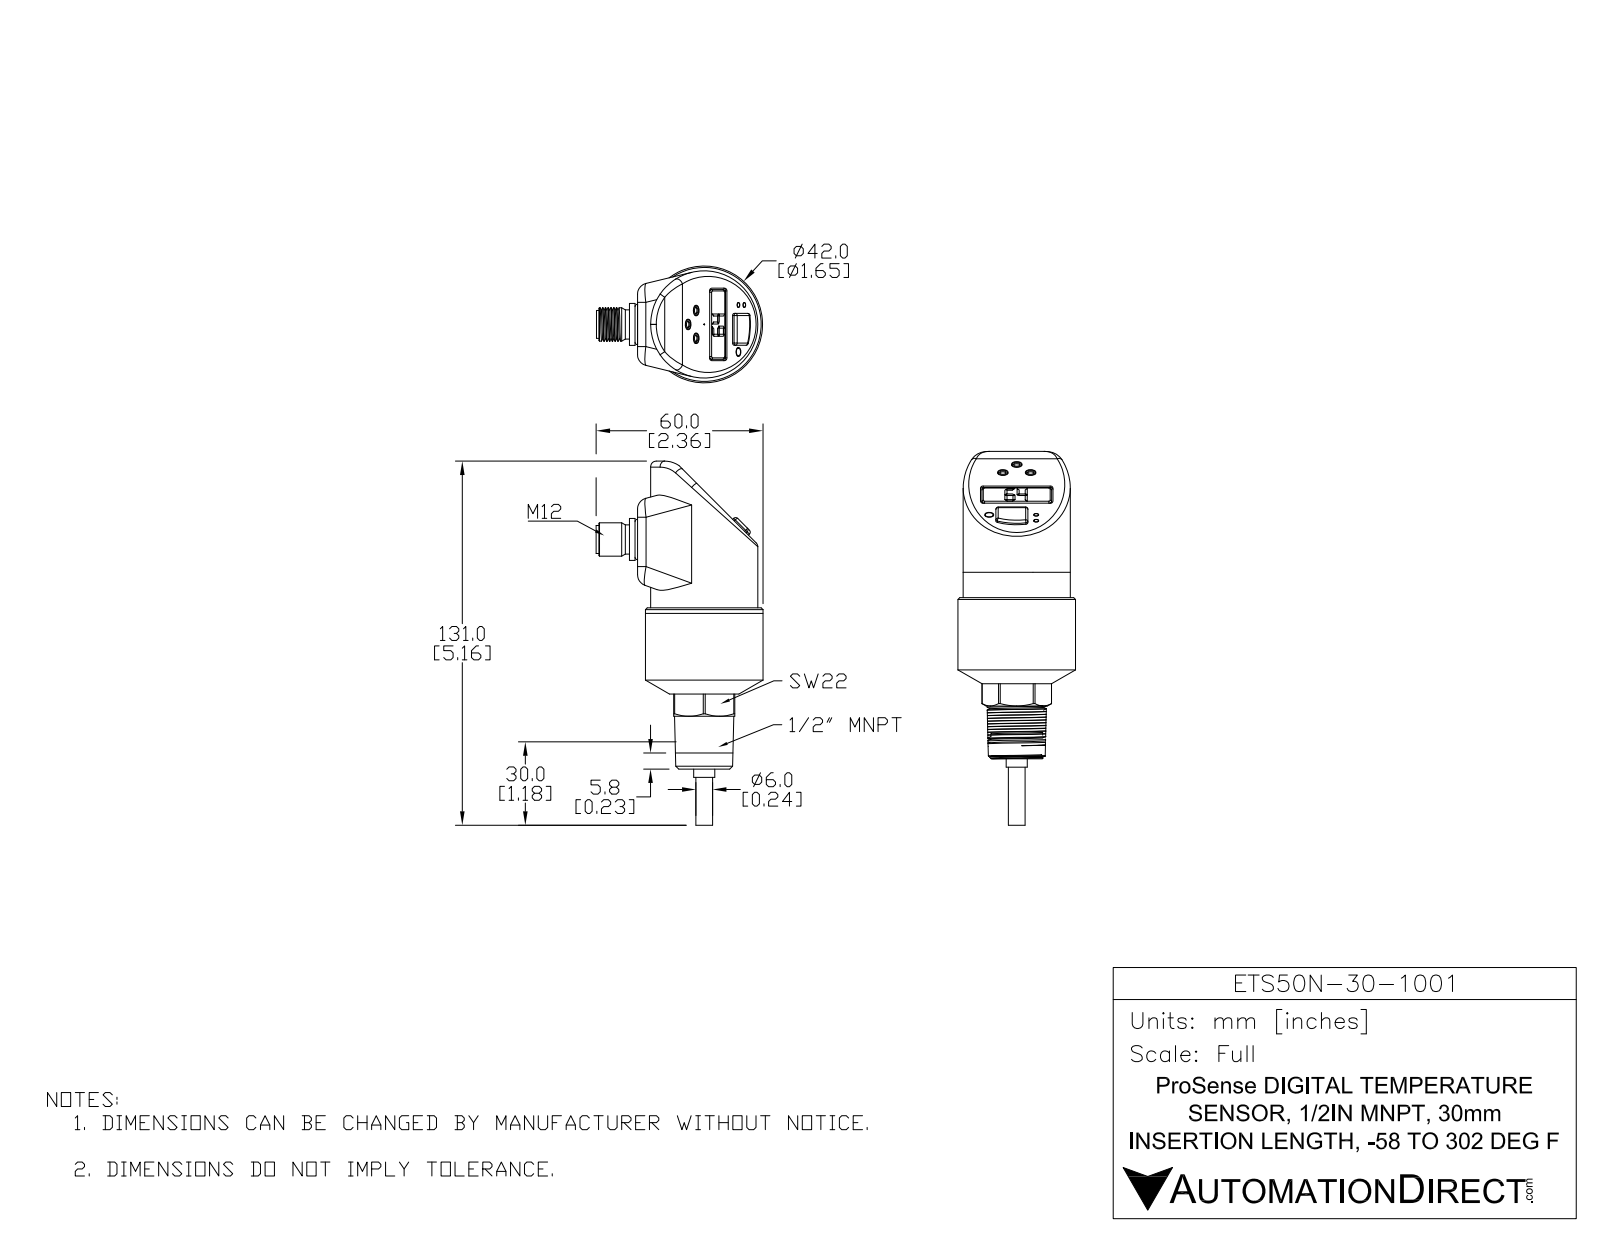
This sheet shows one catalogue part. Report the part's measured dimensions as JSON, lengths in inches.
{"part_name": "ETS50N-30-1001", "step_written_by": "SolidWorks 2016 (AUTOMOTIVE_DESIGN)", "units": "inches", "bodies": {"solids": 1, "faces": 324, "planar": 138, "cylindrical": 95, "other": 91}, "overall_size": [5.295, 2.36, 1.665], "volume_in3": 6.54, "surface_area_in2": 28.43, "round_holes": [[0.333, 1], [0.433, 1]], "round_bosses_or_shafts": [[0.055, 4], [0.039, 4], [1.665, 1], [1.518, 1], [0.594, 1], [0.573, 1], [0.472, 1], [0.413, 1]], "partial_cylinders_radius": [[0.039, 8], [0.031, 7], [0.02, 4], [0.157, 4], [0.276, 4], [0.024, 1], [0.079, 1], [0.355, 1]], "face_to_face_distances": [0.866, 2.283, 0.547, 0.512, 0.035, 0.079, 0.114, 0.626, 1.492, 1.378]}
